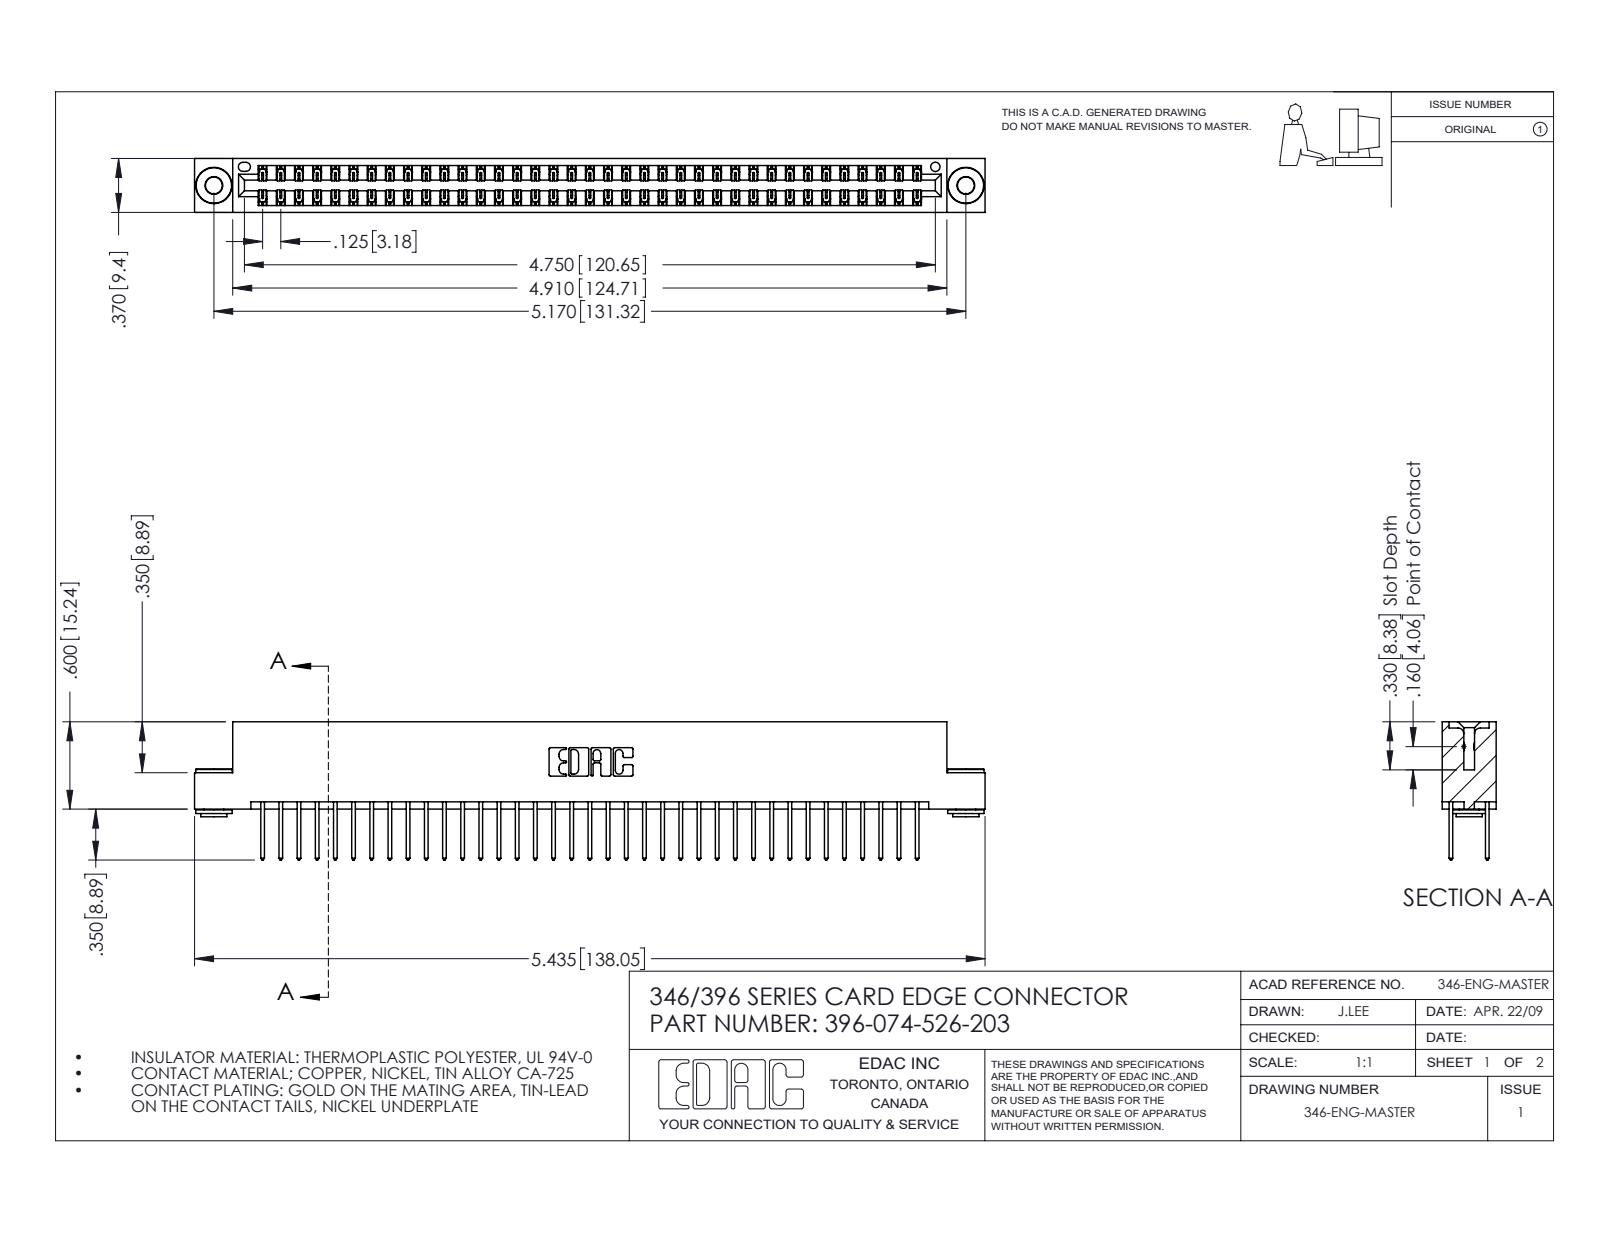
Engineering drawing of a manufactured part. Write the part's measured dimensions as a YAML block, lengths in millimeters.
part_name: "396-074-526-203; 345-292-001_345-293-126; 345-250-002_345-250-002-102; 346 Part_Flush Mounting Lugs - 0.156 Dia-TH"
step_written_by: "SolidWorks 2016 (CONFIG_CONTROL_DESIGN)"
units: millimeters
bodies: {solids: 77, faces: 4008, planar: 2676, cylindrical: 1324, other: 8}
overall_size: [138, 24.1, 9.4]
volume: 13600
surface_area: 19320
round_holes:
  - {diameter: 2.9, count: 2}
  - {diameter: 4, count: 2}
  - {diameter: 1.6, count: 1}
round_bosses_or_shafts:
  - {diameter: 6.4, count: 2}
  - {diameter: 4.6, count: 2}
  - {diameter: 3.5, count: 2}
partial_cylinders:
  - {radius: 0.2, count: 111}
  - {radius: 0.3, count: 74}
  - {radius: 0.3, count: 22}
  - {radius: 0.2, count: 6}
  - {radius: 0.8, count: 6}
  - {radius: 0.7, count: 3}
  - {radius: 0.4, count: 2}
  - {radius: 0.6, count: 2}
face_to_face_distances: [1.2, 8.2, 6.4, 9.4, 0.6, 1.8, 7.6, 7, 3.8, 5.6]
hole_center_spacings: [6.2, 126, 131.3]
